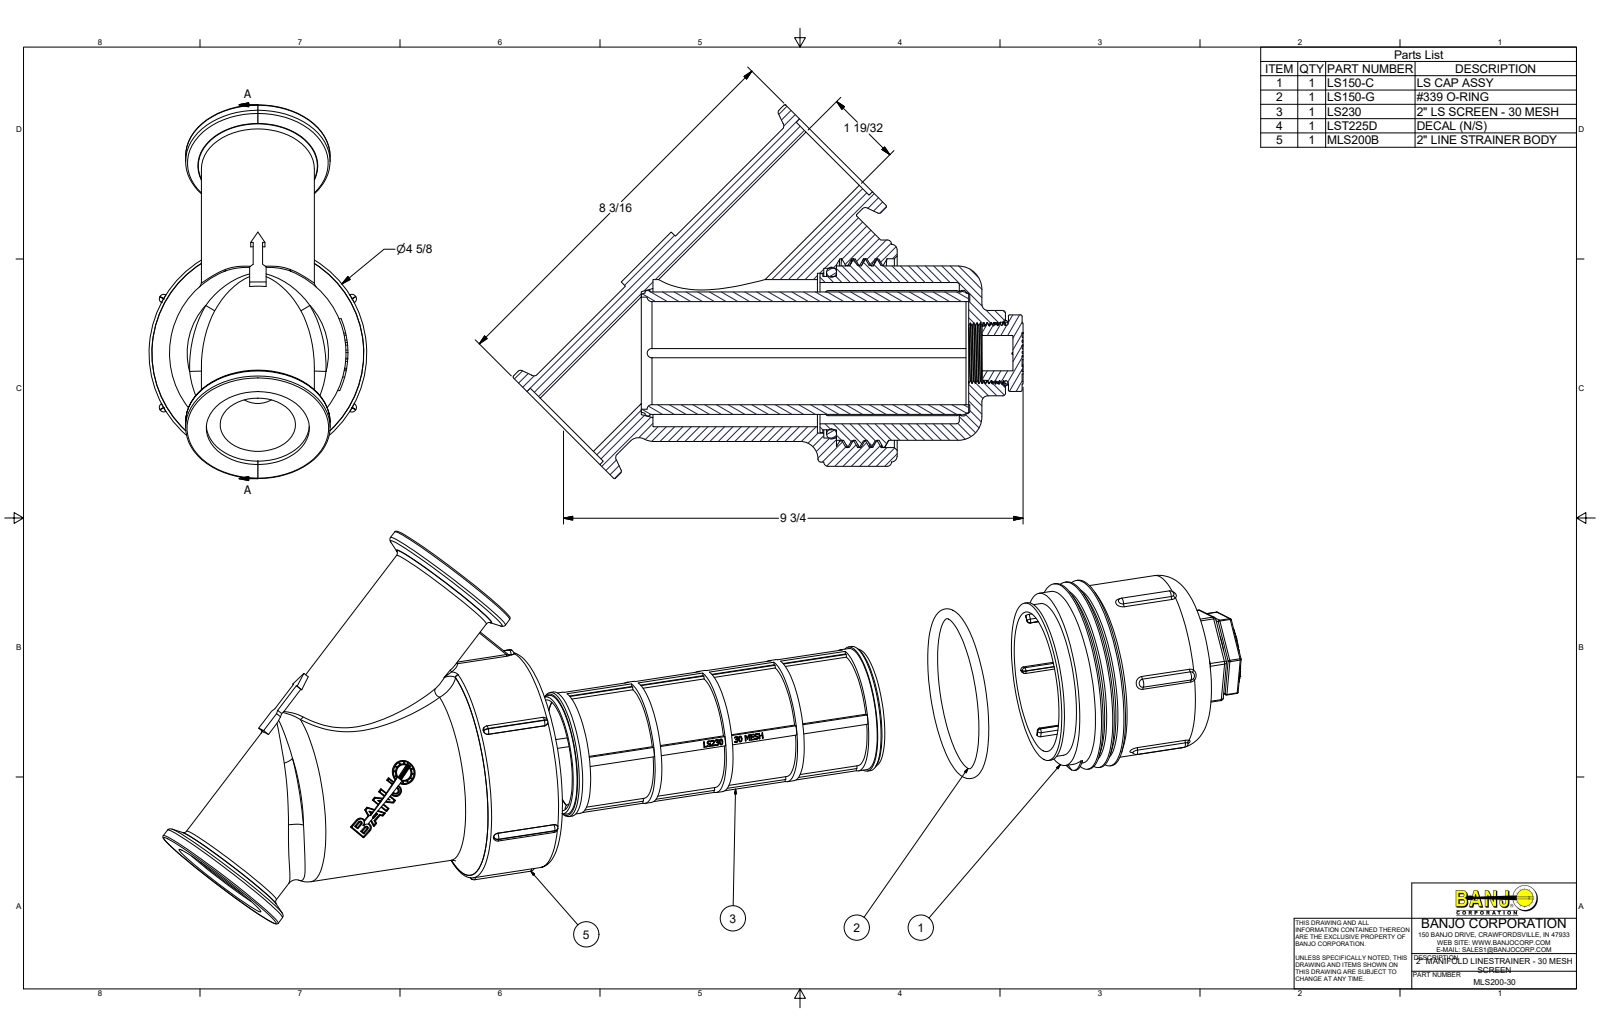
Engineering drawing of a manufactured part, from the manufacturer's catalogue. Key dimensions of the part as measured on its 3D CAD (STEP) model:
Part name (STEP PRODUCT): MLS200B; LS150XC; LSQ200-PL; LSQ200-R (+4 more)
STEP written by: Autodesk Inventor 2014 (AUTOMOTIVE_DESIGN)
Units: millimetres
Bodies: 5 solids, 1330 faces (656 planar, 251 cylindrical, 423 other)
Overall size (bounding box): 275.29 × 201.6 × 117.47
Volume: 926 674 mm³ · Surface area: 310 032 mm²
Round holes (diameter × count): ⌀55.63 ×3, ⌀40.64 ×2, ⌀8.36 ×1, ⌀11.81 ×1, ⌀19.05 ×1, ⌀29.87 ×1, ⌀59.69 ×1, ⌀76.2 ×1, ⌀79.38 ×1, ⌀86.23 ×1, ⌀91.57 ×1, ⌀94.73 ×1
Round bosses / shafts (diameter × count): ⌀77.98 ×2, ⌀117.47 ×1, ⌀95.25 ×1, ⌀94.04 ×1, ⌀85.85 ×1, ⌀82.73 ×1, ⌀67.72 ×1, ⌀66.04 ×1
Partial cylindrical surfaces — rounded edges, fillets, slot ends (radius × count): R1.52 ×46, R2.29 ×35, R0.76 ×24, R2.38 ×6, R3.17 ×6, R2.54 ×4, R0.72 ×2, R1.04 ×2
Main face-to-face distances: 71.37, 2.54, 205.45, 207.99, 36.7, 5.08, 105.39, 176.76, 40.51, 81.03
